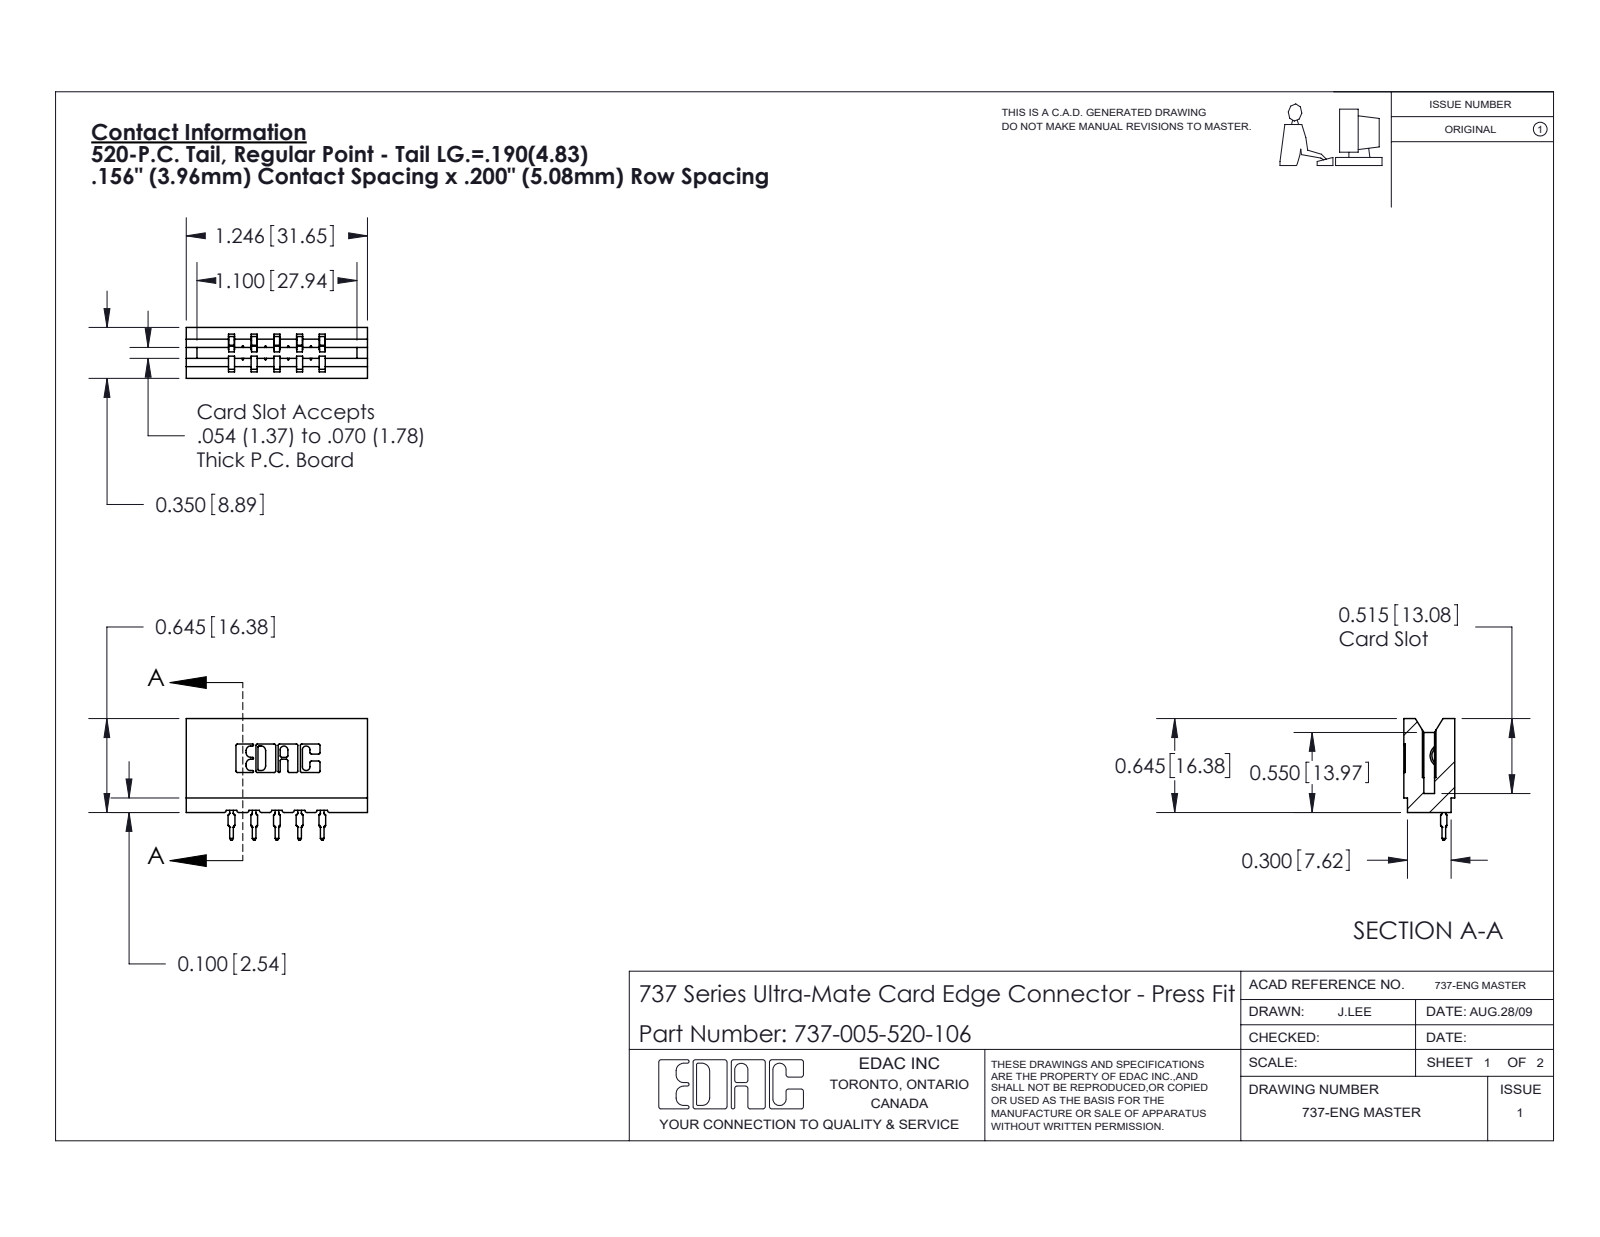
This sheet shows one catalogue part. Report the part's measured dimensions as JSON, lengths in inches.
{"part_name": "745-292-001_520; 737 Part_Insulator Option - 06; 737-005-520-106", "step_written_by": "SolidWorks 2020 (CONFIG_CONTROL_DESIGN)", "units": "inches", "bodies": {"solids": 6, "faces": 660, "planar": 395, "cylindrical": 135, "other": 130}, "overall_size": [1.246, 0.836, 0.35], "volume_in3": 0.201, "surface_area_in2": 5.747, "partial_cylinders_radius": [[0.01, 22], [0.015, 10], [0.021, 10], [0.007, 6], [0.031, 6], [0.005, 4], [0.011, 4], [0.026, 3]], "face_to_face_distances": [0.138, 0.212, 0.156, 0.35, 0.312, 0.198, 0.074, 0.354, 0.042, 0.025]}
